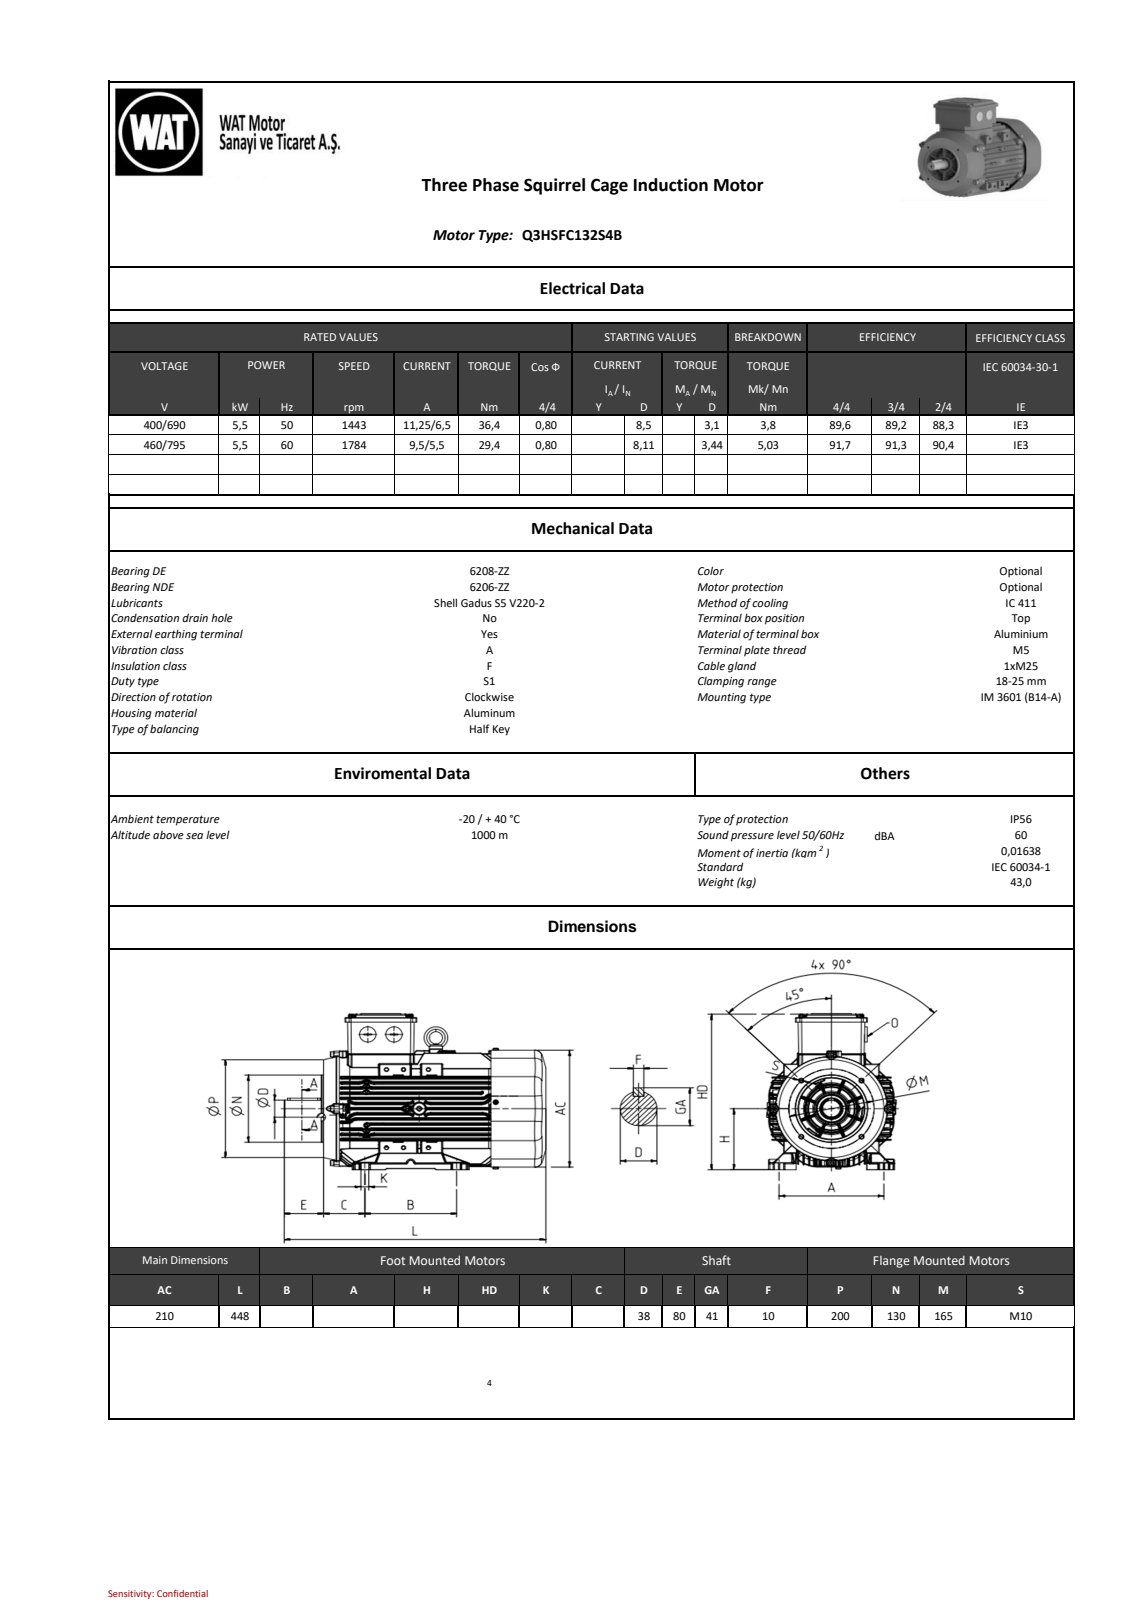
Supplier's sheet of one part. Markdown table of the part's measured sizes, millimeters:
| quantity | value |
| --- | --- |
| part name | Ar311510F8055401 |
| STEP written by | SIEMENS PLM Software NX 9.0 (AUTOMOTIVE_DESIGN) |
| units | millimeters |
| bodies | 0 solids, 7828 faces (1521 planar, 2455 cylindrical, 3852 other) |
| overall size | 422 × 259.07 × 219 |
| round holes (diameter × count) | 8.5 × 4, 12 × 2, 27.8 × 2, 4 × 1, 4.72 × 1, 8 × 1, 10.3 × 1, 13 × 1, 57.4 × 1, 58.67 × 1 |
| round bosses / shafts (diameter × count) | 8 × 8, 11.8 × 4, 10 × 4, 6 × 4, 188 × 1, 130 × 1, 61 × 1, 40 × 1 |
| partial cylindrical surfaces (radius × count) | 0.5 × 758, 0.8 × 511, 1 × 205, 2 × 140, 3 × 37, 0.38 × 13, 4 × 8, 0.75 × 6 |
| main face-to-face distances | 1, 10.99, 21.5, 35.96, 99.54, 24.97, 90.43, 68.93, 112.88, 8.16 |
| hole center spacings | 40, 82.51, 116.68, 165.01 |
